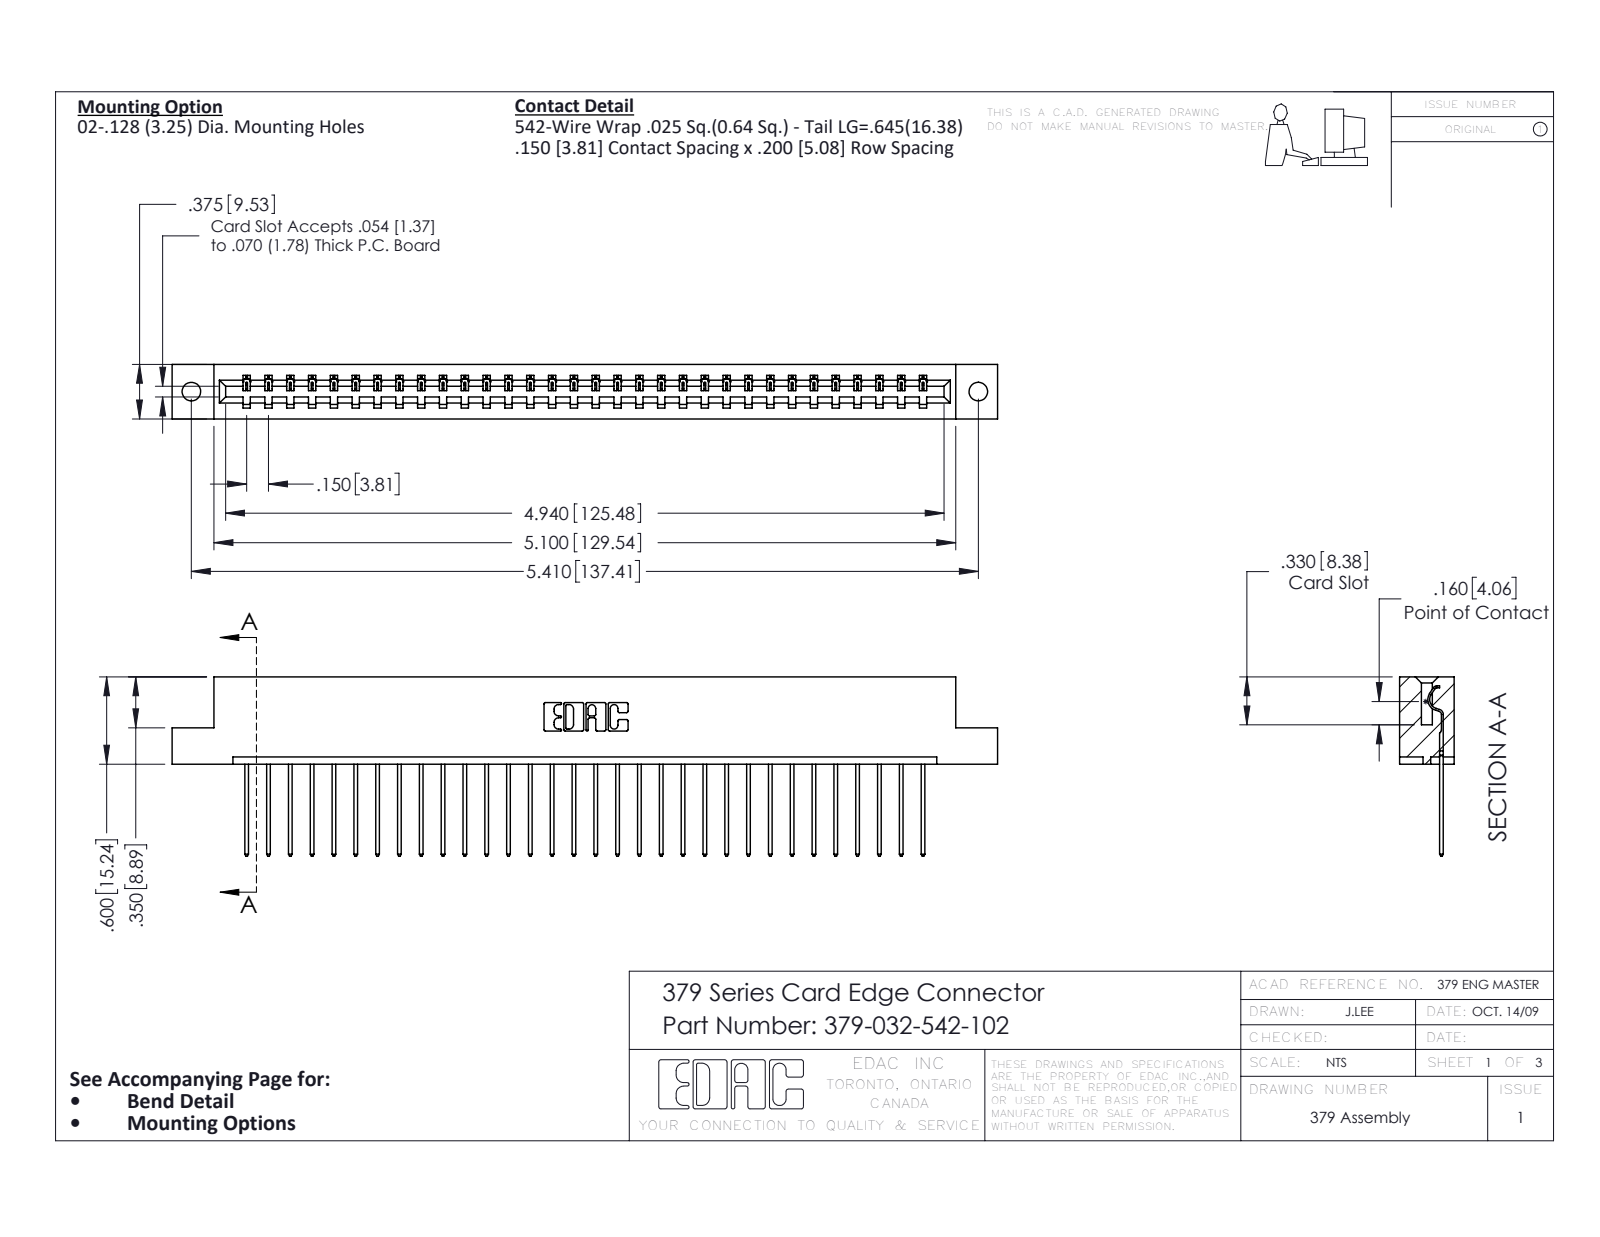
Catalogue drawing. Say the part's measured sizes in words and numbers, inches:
The part is named "379-032-542-102; 379 Part_Flush - .128 Dia; 345-292-001_345-293-142". Its 3-D file was written by "SolidWorks 2016 (CONFIG_CONTROL_DESIGN)". It is 33 solids with 1970 faces: 1414 planar, 556 cylindrical and 0 other. Overall it measures 5.675 by 1.232 by 0.375 inches. Its volume is 0.919 cubic inches and its surface area 24.11 square inches. Round holes: 2 of diameter 0.128. Partial cylindrical surfaces (rounded edges, fillets, slot ends): 64 of radius 0.006, 64 of radius 0.01, 22 of radius 0.01, 6 of radius 0.007, 6 of radius 0.031, 3 of radius 0.026, 1 of radius 0.014, 1 of radius 0.022. The main face-to-face distances are 0.3, 0.075, 0.375, 0.225, 0.275, 0.1, 0.025, 0.2, 0.6, 0.55. The hole center spacings are 5.41.
